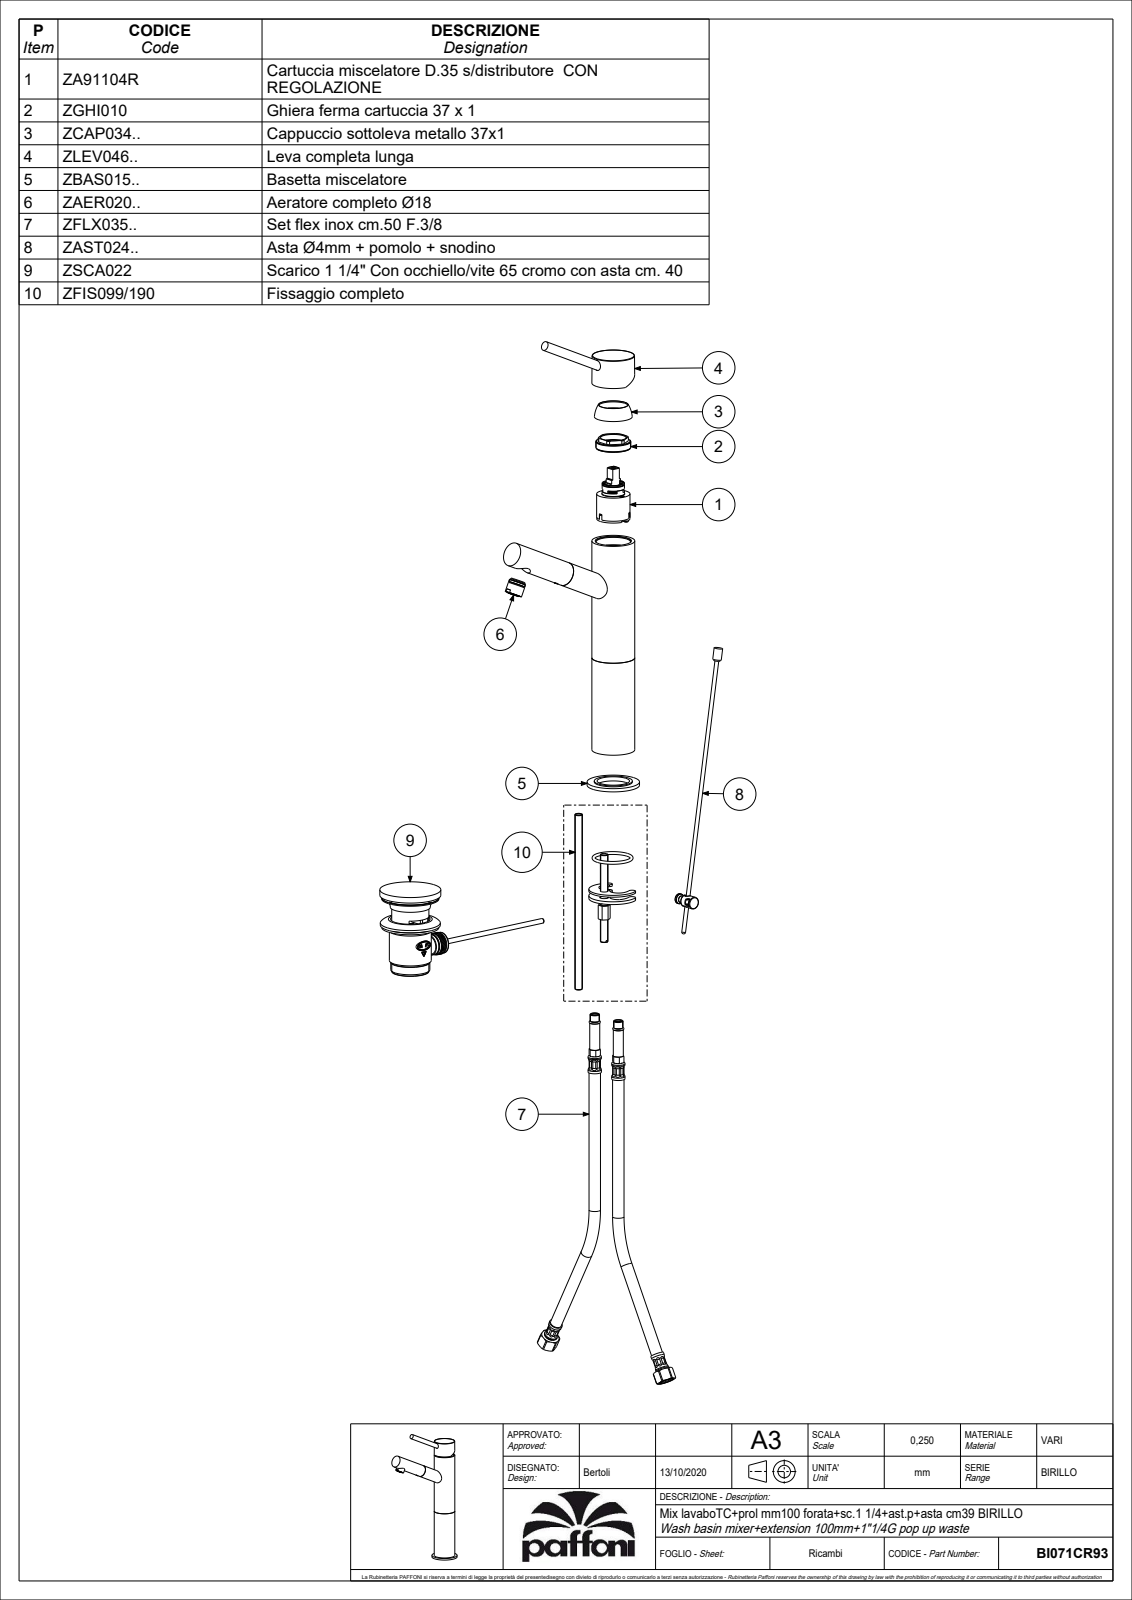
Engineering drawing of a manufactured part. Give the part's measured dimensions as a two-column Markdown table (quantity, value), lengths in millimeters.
| quantity | value |
| --- | --- |
| part name | BI071CR93 |
| STEP written by | CREO PARAMETRIC BY PTC INC, 2020044 (CONFIG_CONTROL_DESIGN) |
| units | millimeters |
| bodies | 0 solids, 159 faces (36 planar, 48 cylindrical, 75 other) |
| overall size | 292.84 × 171.44 × 55 |
| round holes (diameter × count) | 5 × 1, 5.5 × 1 |
| round bosses / shafts (diameter × count) | 25 × 2, 55 × 1, 45 × 1, 18 × 1, 12.5 × 1, 9.6 × 1 |
| partial cylindrical surfaces (radius × count) | 0.5 × 24, 5 × 1, 9.2 × 1 |
| main face-to-face distances | 3.5, 230.5, 227, 243.5, 240, 13, 258.6, 255.1, 28.1, 15.1 |
